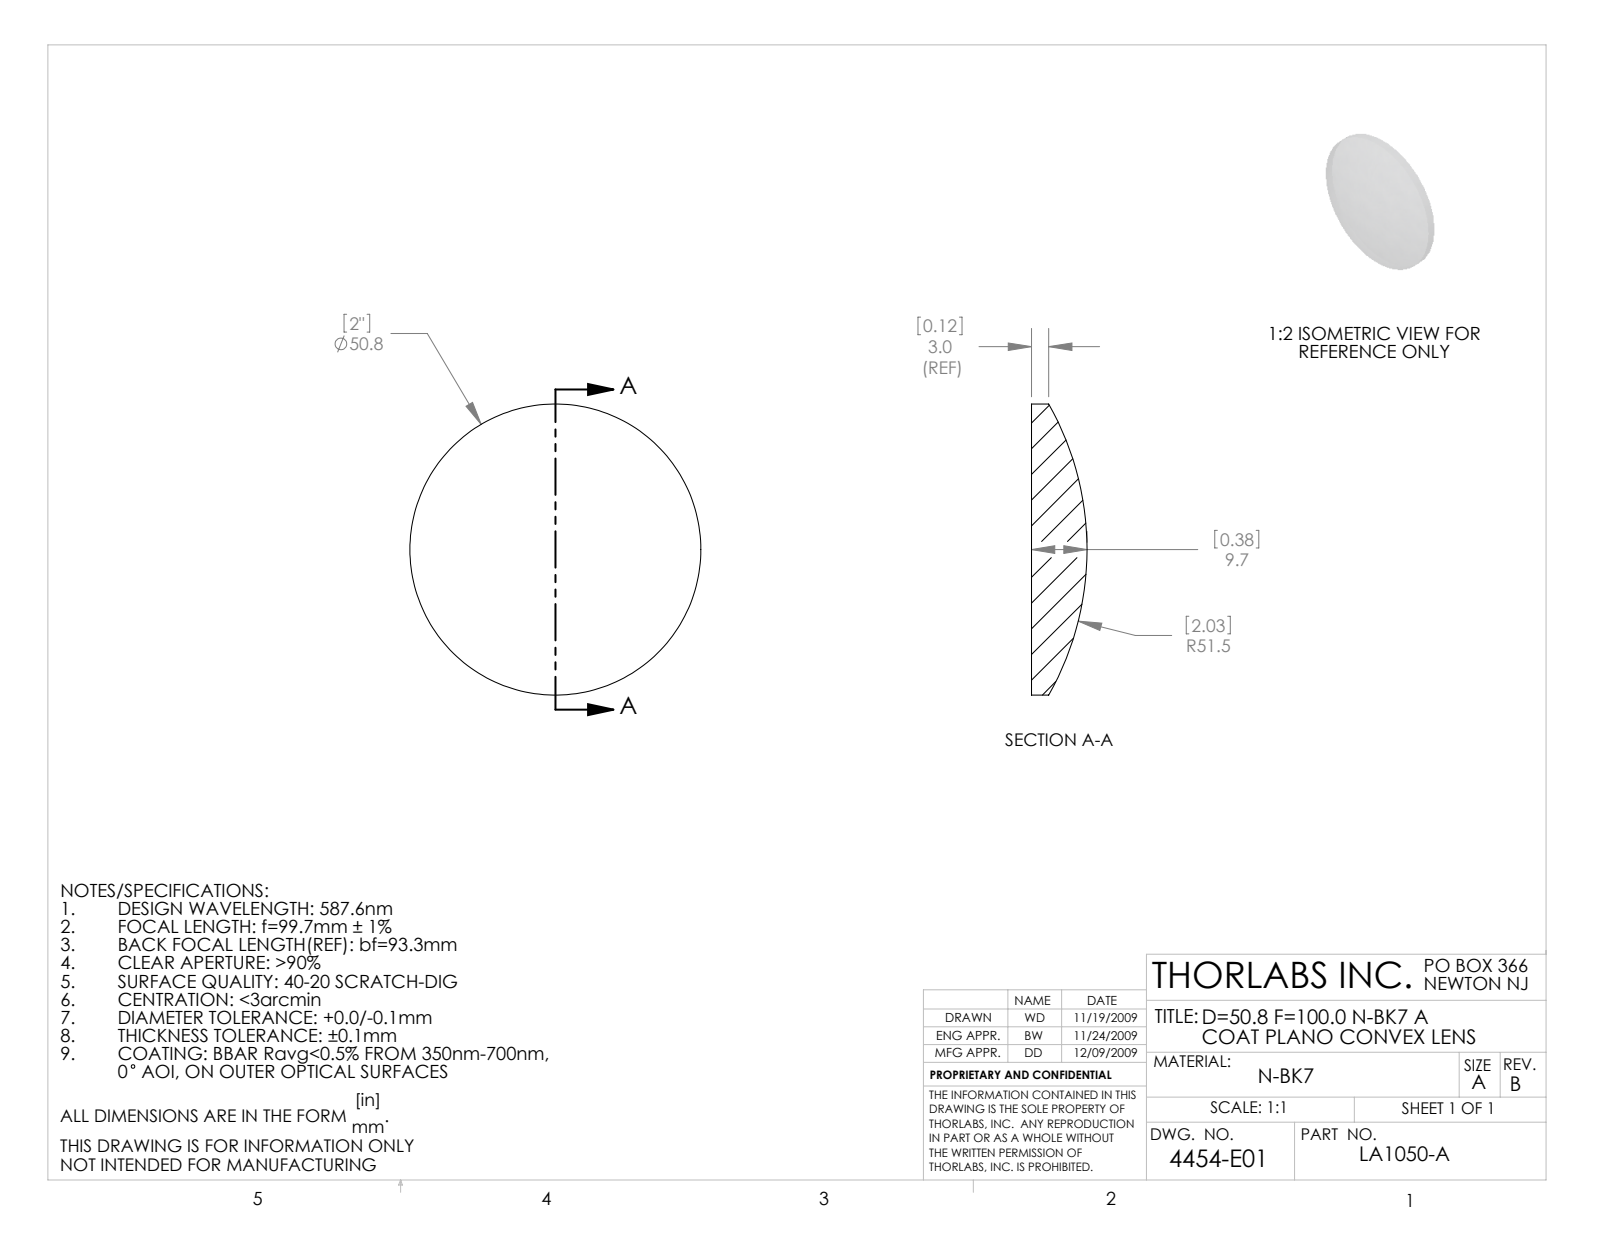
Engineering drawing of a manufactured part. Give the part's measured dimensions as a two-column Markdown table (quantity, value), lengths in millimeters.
| quantity | value |
| --- | --- |
| part name | 4454-E0W |
| STEP written by | SolidWorks 2009 (AUTOMOTIVE_DESIGN) |
| units | millimeters |
| bodies | 1 solid, 5 faces (1 planar, 2 cylindrical, 2 other) |
| overall size | 50.8 × 50.8 × 9.69 |
| volume | 13 008 mm³ |
| surface area | 4 672 mm² |
| round bosses / shafts (diameter × count) | 50.8 × 1 |
